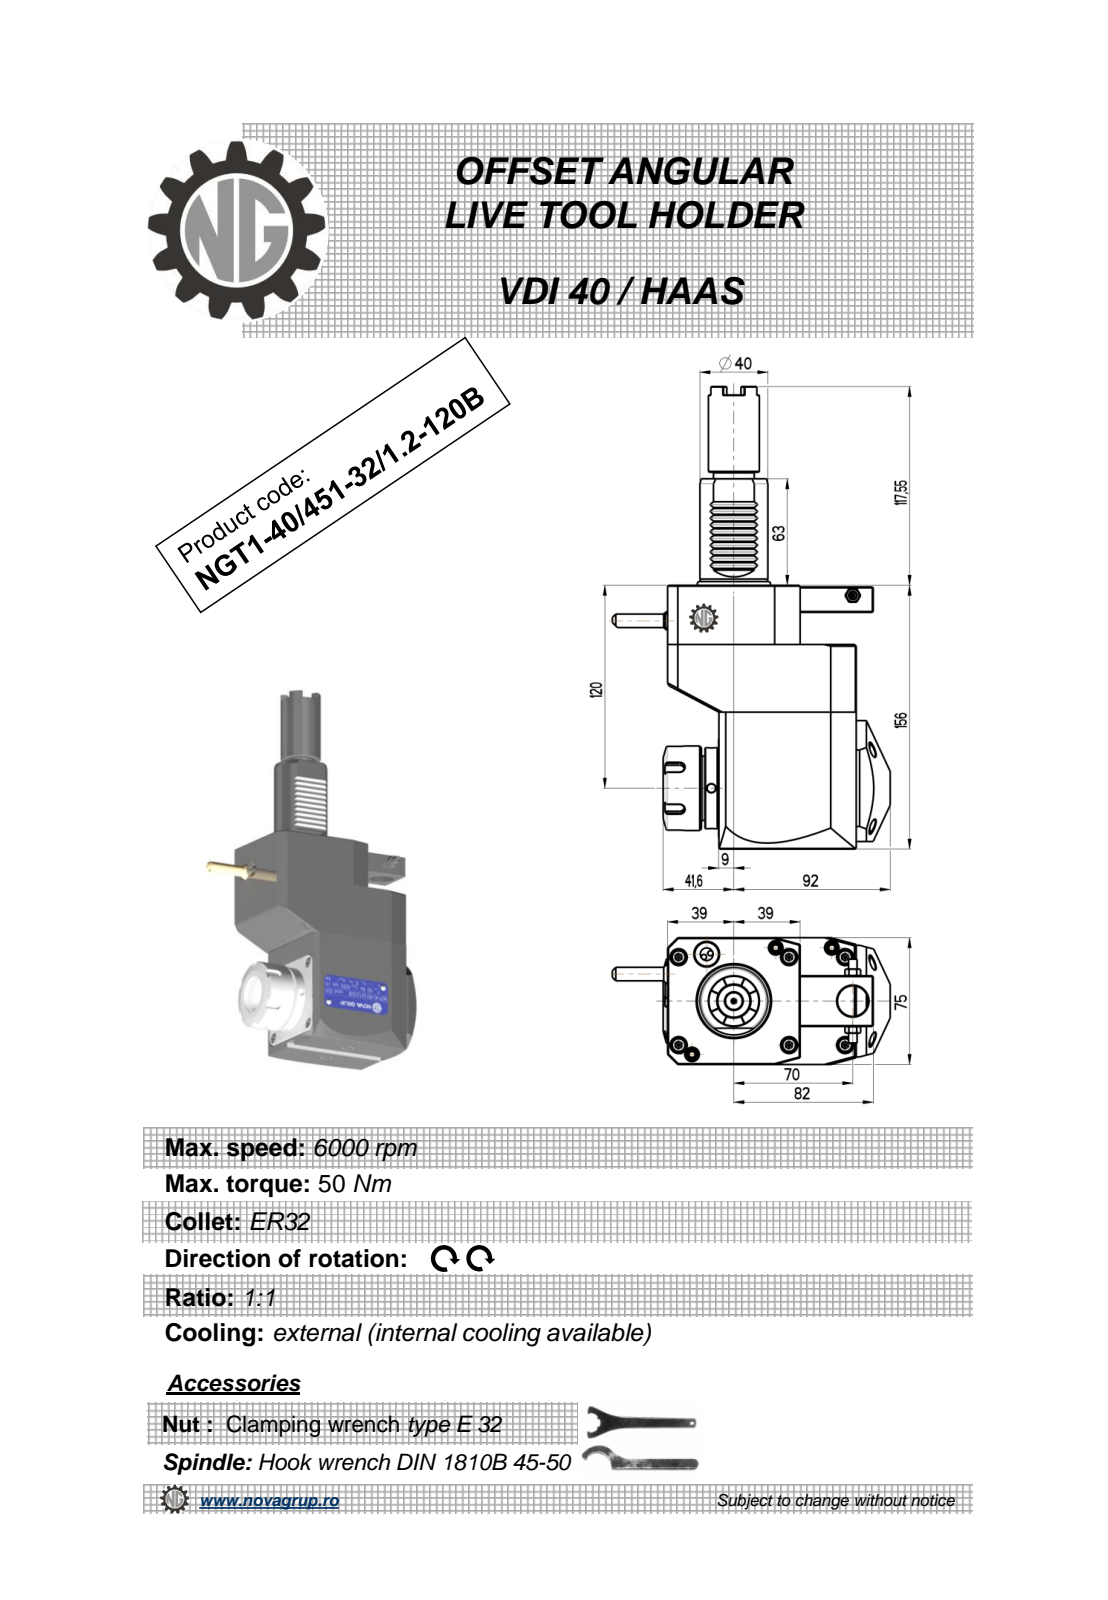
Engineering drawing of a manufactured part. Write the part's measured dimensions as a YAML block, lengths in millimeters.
part_name: "NGT1_40_451_32_1_2_120B"
step_written_by: "PRO/ENGINEER BY PARAMETRIC TECHNOLOGY CORPORATION, 2010280 (CONFIG_CONTROL_DESIGN)"
units: millimeters
bodies: {solids: 1, faces: 464, planar: 230, cylindrical: 97, other: 137}
overall_size: [273.55, 163.5, 76.6]
volume: 1231000
surface_area: 94717
round_holes:
  - {diameter: 5, count: 3}
  - {diameter: 3, count: 1}
  - {diameter: 4.2, count: 1}
  - {diameter: 9.5, count: 1}
  - {diameter: 18, count: 1}
  - {diameter: 26.8, count: 1}
  - {diameter: 27, count: 1}
round_bosses_or_shafts:
  - {diameter: 50, count: 1}
  - {diameter: 48, count: 1}
  - {diameter: 41, count: 1}
  - {diameter: 40, count: 1}
  - {diameter: 30, count: 1}
  - {diameter: 26.58, count: 1}
  - {diameter: 24, count: 1}
  - {diameter: 10, count: 1}
partial_cylinders:
  - {radius: 0.26, count: 12}
  - {radius: 0.3, count: 10}
  - {radius: 0.2, count: 6}
  - {radius: 3, count: 5}
  - {radius: 0.5, count: 1}
  - {radius: 9.75, count: 1}
  - {radius: 40, count: 1}
face_to_face_distances: [75, 156, 111, 30, 121, 35, 81, 48, 33, 78]
hole_center_spacings: [13.25, 20.93, 70, 83.25, 100.28, 112.5, 141.16]
